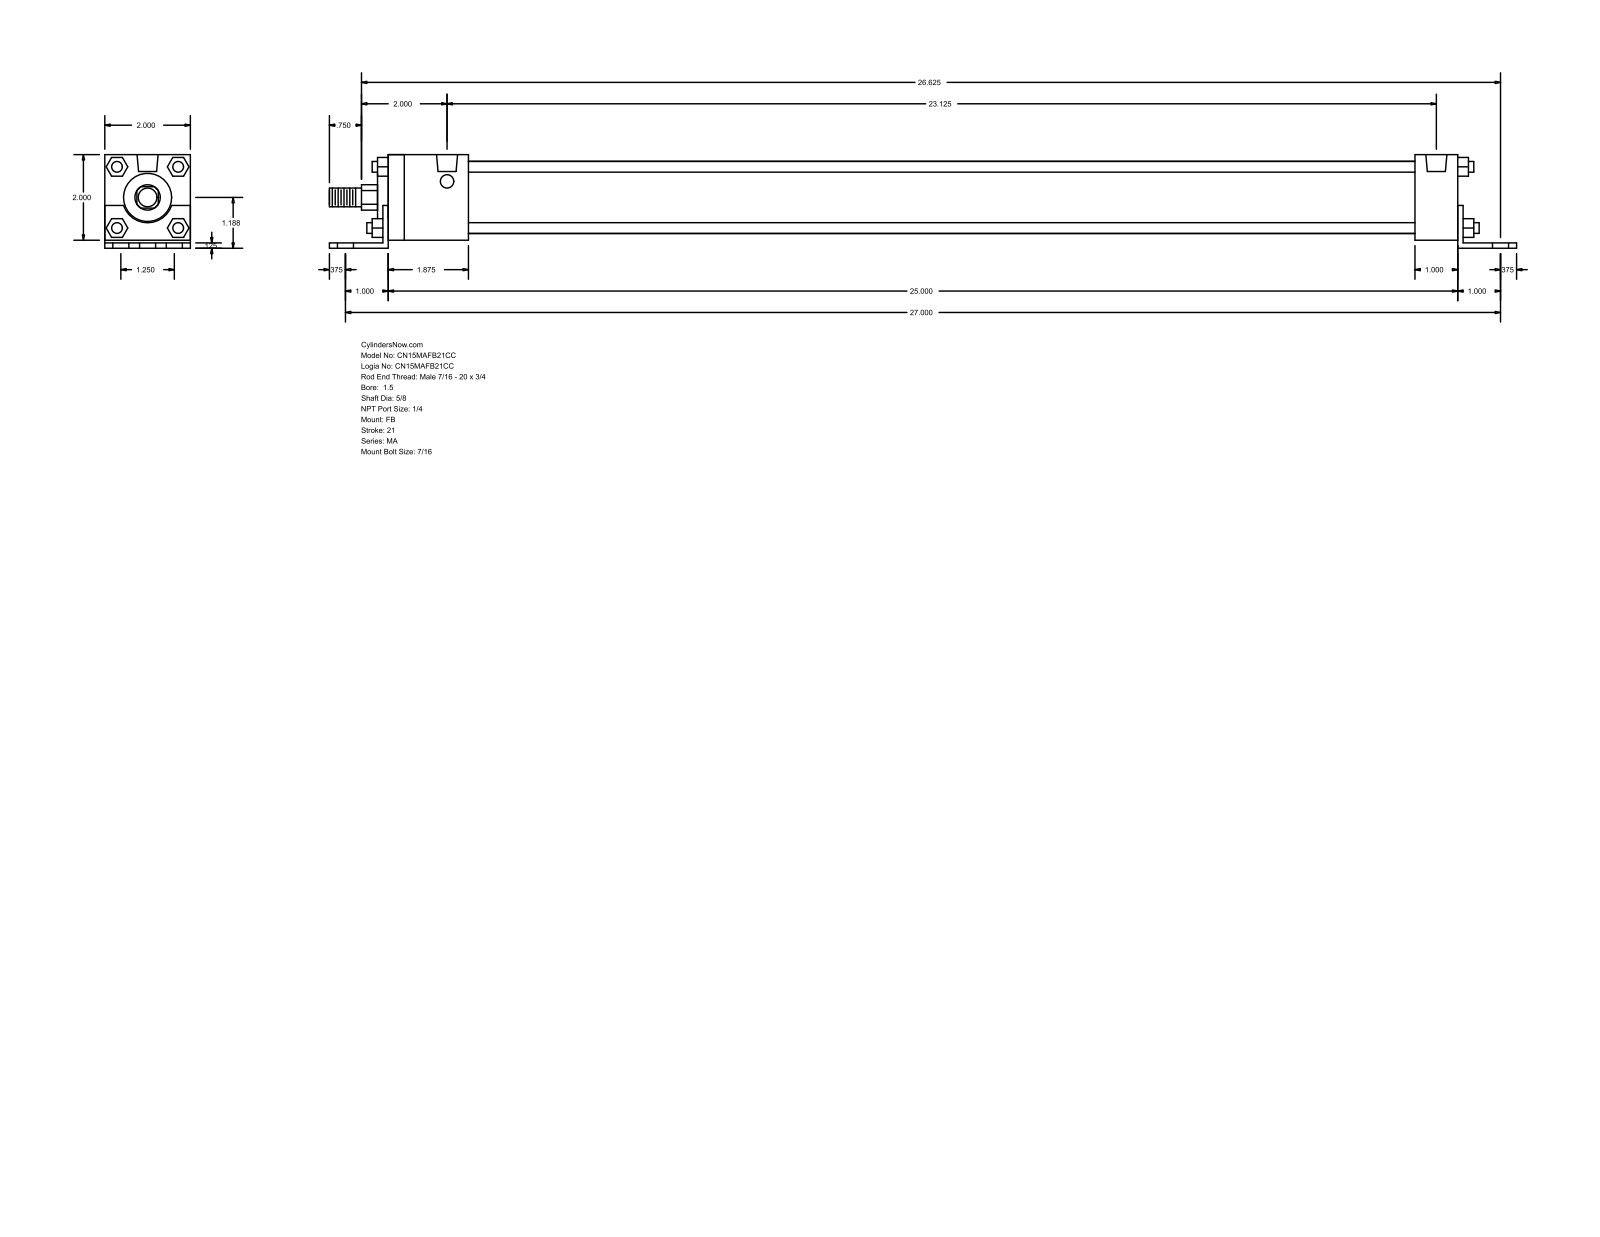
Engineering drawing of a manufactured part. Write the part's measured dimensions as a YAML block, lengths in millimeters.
part_name: "MA_FB__0150_0.625"
step_written_by: "GSSL Pune (CONFIG_CONTROL_DESIGN)"
units: millimeters
bodies: {solids: 0, faces: 140, planar: 105, cylindrical: 35, other: 0}
overall_size: [704.85, 55.56, 50.8]
round_holes:
  - {diameter: 11.11, count: 6}
  - {diameter: 7.94, count: 4}
  - {diameter: 12.49, count: 2}
round_bosses_or_shafts:
  - {diameter: 6.35, count: 4}
  - {diameter: 42.93, count: 1}
  - {diameter: 28.57, count: 1}
  - {diameter: 15.88, count: 1}
  - {diameter: 11.11, count: 1}
partial_cylinders:
  - {radius: 7.54, count: 1}
  - {radius: 15.05, count: 1}
face_to_face_distances: [50.8, 3.17, 4.76, 55.56, 1.59, 52.39, 25.4, 641.35, 6.35, 3.18]
hole_center_spacings: [15.88, 685.98, 685.8, 31.76, 41.28, 62.38, 587.37, 625.67]
